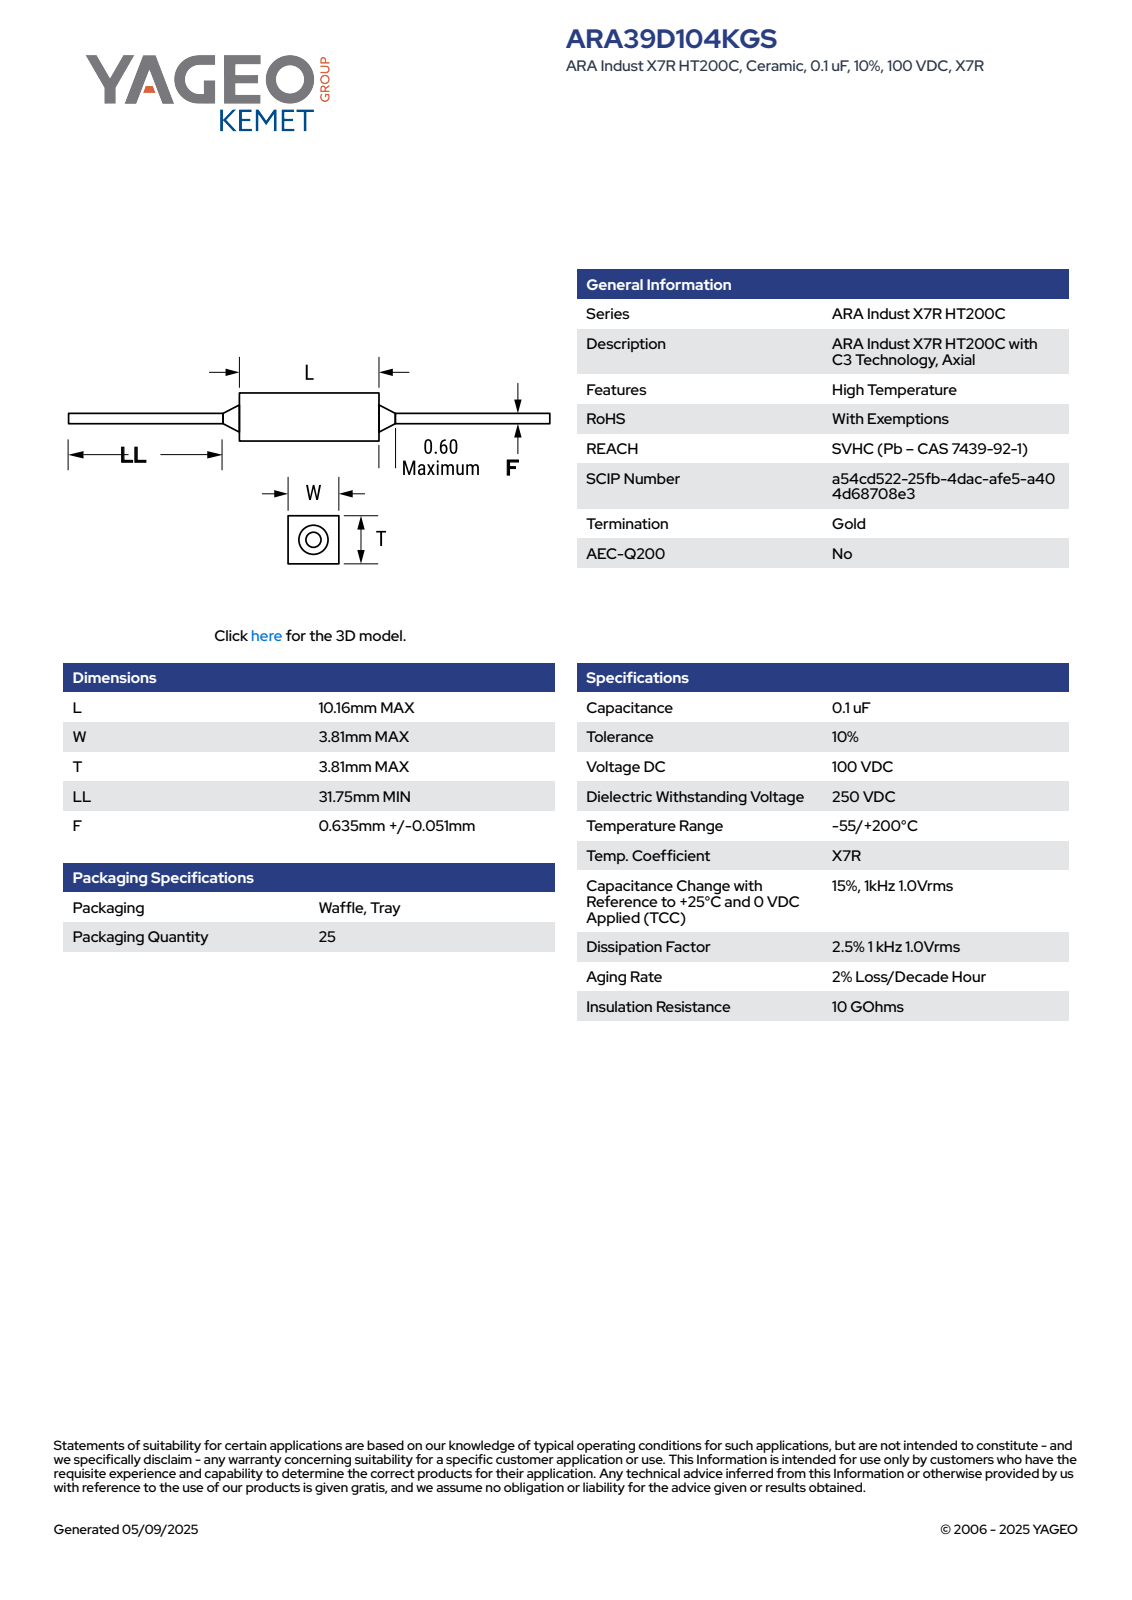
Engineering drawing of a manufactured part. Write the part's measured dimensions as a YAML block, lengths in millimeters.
part_name: "CCR_C3_39_L10.16T3.81LL3.175F0.686W3.81"
step_written_by: "SolidWorks 2021 (AUTOMOTIVE_DESIGN)"
units: millimeters
bodies: {solids: 4, faces: 73, planar: 65, cylindrical: 4, other: 4}
overall_size: [16.98, 3.81, 3.81]
volume: 150
surface_area: 213
round_bosses_or_shafts:
  - {diameter: 0.69, count: 1}
face_to_face_distances: [3.81, 3.82, 10.16, 3.41, 13.57, 16.98, 2.6, 1.22, 1, 1.6]
